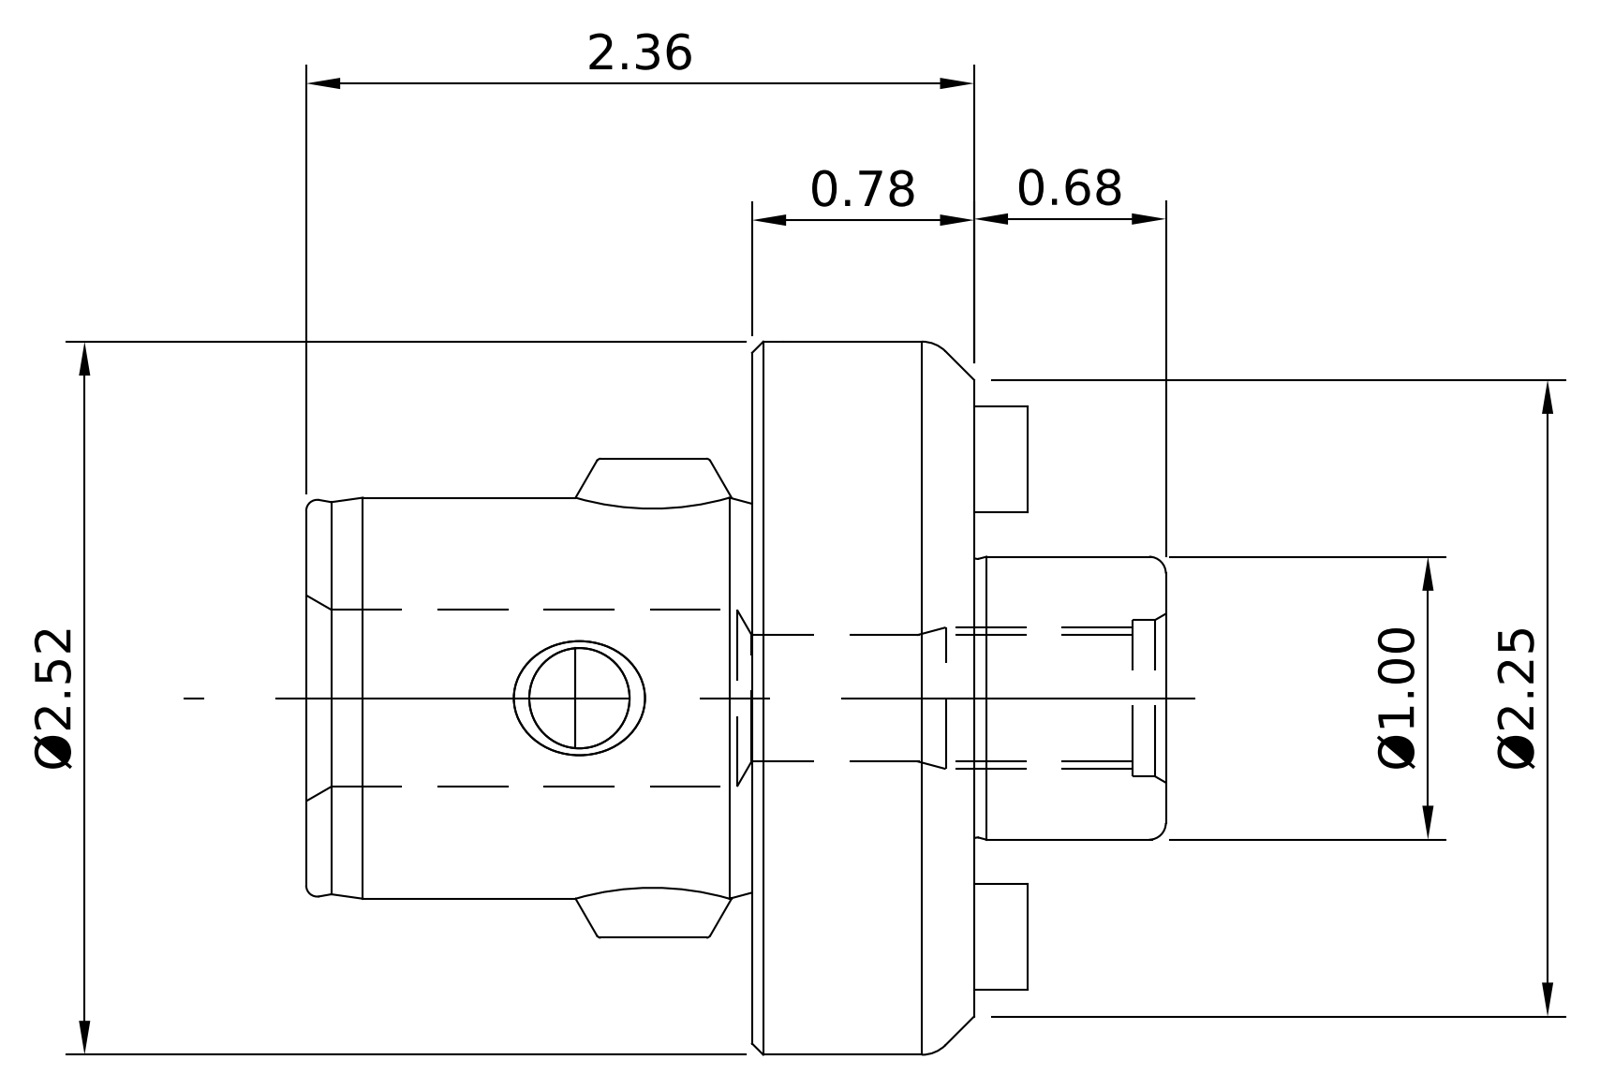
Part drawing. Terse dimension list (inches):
name: 11.335.403; 11.691.622; 10.691.50X_10.691.506
written by: SolidWorks 2011 (CONFIG_CONTROL_DESIGN)
unit: in
bodies: 4 solids, 133 faces (37 planar, 42 cylindrical, 54 other)
size: 3.048 × 2.52 × 2.52
volume: 6.256 in³; area: 36.51 in²
holes: 2× ⌀0.375, 1× ⌀0.354, 1× ⌀0.453, 1× ⌀0.551, 1× ⌀0.567, 1× ⌀0.63, 1× ⌀0.728
bosses: 2× ⌀0.375, 1× ⌀2.52, 1× ⌀1.417, 1× ⌀1, 1× ⌀0.547, 1× ⌀0.469, 1× ⌀0.39
rounds: 1× R0.709
face distances: 0.784, 1.575, 2.359, 3.048, 1.473, 0.689, 0.375, 2.578, 1.003, 0.219
hole spacings: 0.844, 1.687
